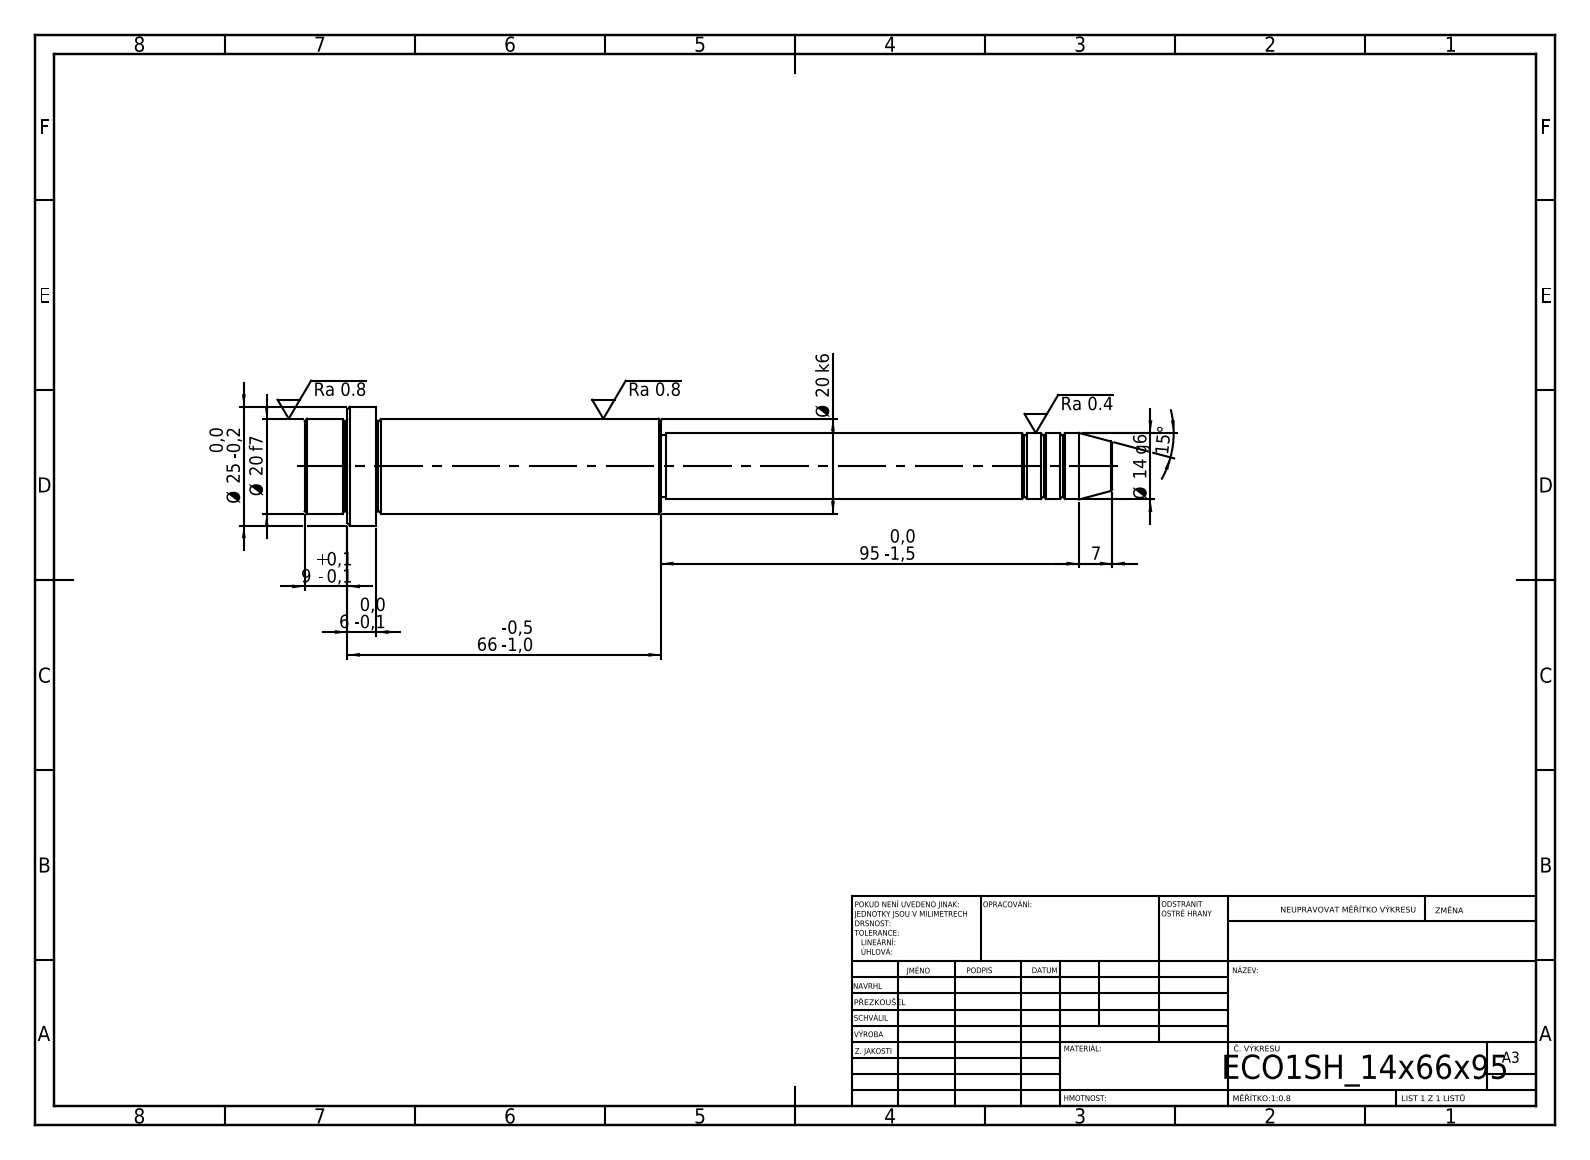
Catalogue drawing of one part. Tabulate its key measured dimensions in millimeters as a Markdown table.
| quantity | value |
| --- | --- |
| STEP written by | SolidWorks 2019 (CONFIG_CONTROL_DESIGN) |
| units | millimeters |
| bodies | 1 solid, 52 faces (6 planar, 16 cylindrical, 30 other) |
| overall size | 170 × 25 × 25 |
| volume | 38 838 mm³ |
| surface area | 9 970 mm² |
| round bosses / shafts (diameter × count) | 25 × 1, 20 × 1, 14 × 1, 13 × 1 |
| main face-to-face distances | 15, 60, 75, 66, 6, 9, 95, 155, 161, 170 |
